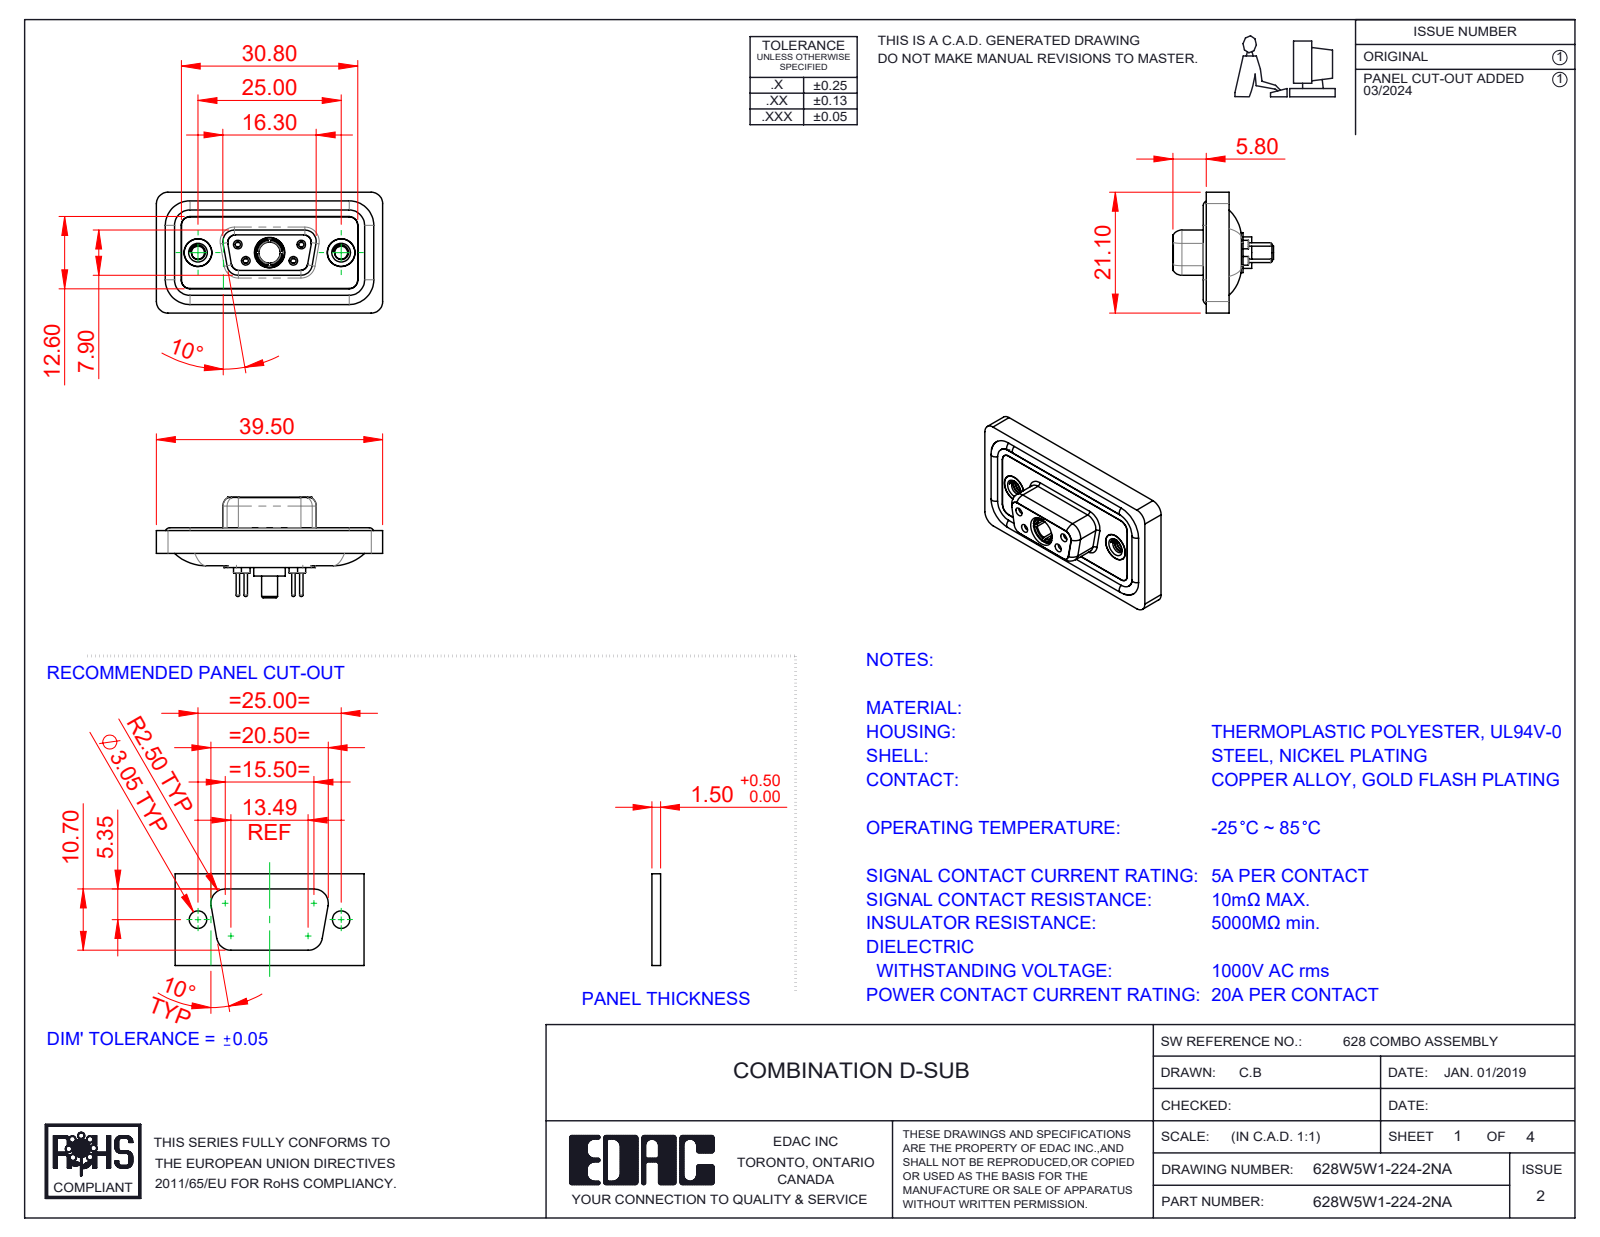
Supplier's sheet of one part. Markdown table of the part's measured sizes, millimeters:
| quantity | value |
| --- | --- |
| part name | 628Combo Threaded Rivet_A; 628Combo Shell Rear_09 Contacts; 628W5W1-224-2NA; 628Combo Waterproof Housing_09 Contacts (+5 more) |
| STEP written by | SolidWorks 2023 (CONFIG_CONTROL_DESIGN) |
| units | millimeters |
| bodies | 13 solids, 678 faces (194 planar, 289 cylindrical, 195 other) |
| overall size | 39.5 × 21.1 × 17.55 |
| volume | 4 769 mm³ |
| surface area | 7 633 mm² |
| round holes (diameter × count) | 0.9 × 4, 1.1 × 4, 1.5 × 4, 2 × 4, 4.85 × 3, 1.6 × 2, 1.7 × 2, 2.26 × 2, 4 × 2, 4.05 × 2, 5 × 2, 3.7 × 1 |
| round bosses / shafts (diameter × count) | 1.6 × 6, 2.2 × 4, 0.6 × 4, 4.95 × 2, 4.8 × 2, 5.5 × 1, 5.2 × 1, 4.96 × 1 |
| partial cylindrical surfaces (radius × count) | 1.5 × 22, 2 × 18, 1.35 × 8, 1.6 × 8, 0.25 × 4, 0.5 × 4, 0.6 × 4, 0.65 × 4 |
| main face-to-face distances | 0.4, 2.9, 1.1, 1.8, 1.6, 0.5, 5.65, 7.45, 5.35, 6.6 |
| hole center spacings | 3.16, 5.72, 7.1, 12.5, 18.1, 4.39, 4.4, 8.31 |
